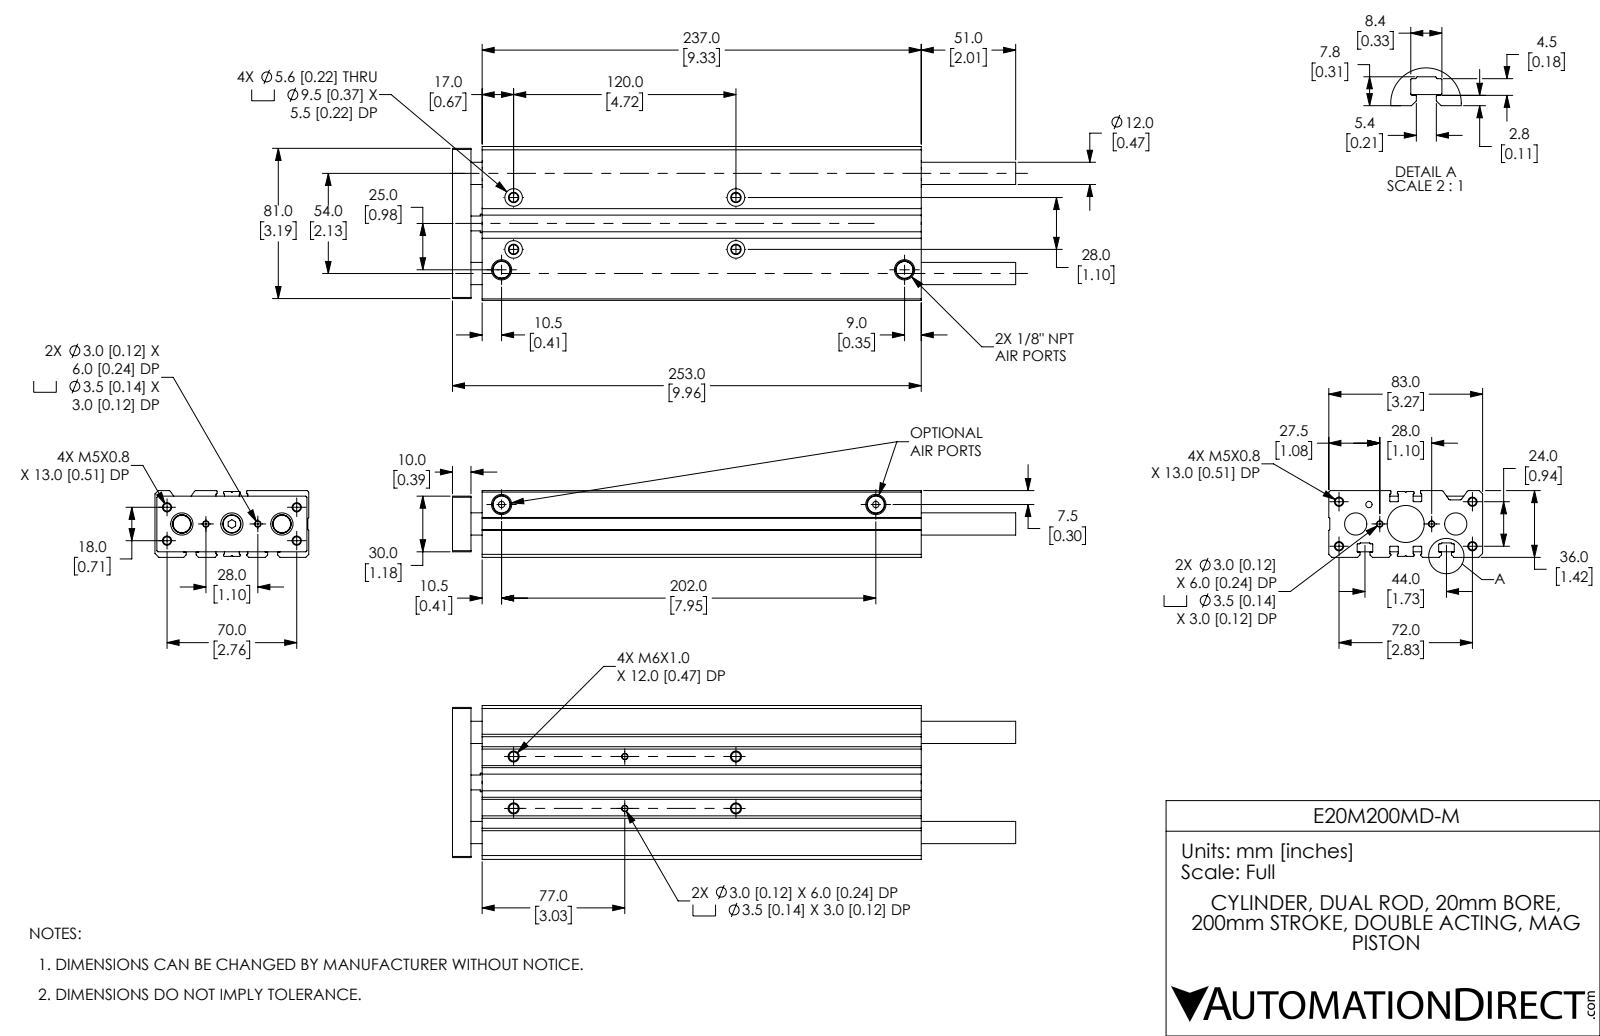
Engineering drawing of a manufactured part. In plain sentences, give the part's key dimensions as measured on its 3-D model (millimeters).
The part is named "E20M200MD-M; E20M200MD-M_BODY; E20M200MD-M_ENDPLATE". Its 3-D file was written by "SolidWorks 2019 (CONFIG_CONTROL_DESIGN)". It is 5 solids with 405 faces: 128 planar, 182 cylindrical and 95 other. Overall it measures 304 by 83 by 36 millimeters. Its volume is 620 753 cubic millimeters and its surface area 161 286 square millimeters. Round holes: 8 of diameter 4.13, 4 of diameter 3, 4 of diameter 3.5, 4 of diameter 4.92, 4 of diameter 5.6, 4 of diameter 9.5, 3 of diameter 6, 3 of diameter 12, 2 of diameter 3.43, 2 of diameter 9.91, 1 of diameter 3.43, 1 of diameter 12. Round bosses or shafts: 1 of diameter 10, 1 of diameter 9.91. Partial cylindrical surfaces (rounded edges, fillets, slot ends): 20 of radius 0.4, 18 of radius 0.2, 10 of radius 0.3, 8 of radius 0.25, 4 of radius 1. The main face-to-face distances are 36, 0.5, 83, 6, 30, 22.2, 45.5, 28.2, 3, 37.5. The hole center spacings are 3.16, 12.04, 15, 21.02, 22.85, 25.06, 28, 36.14.
